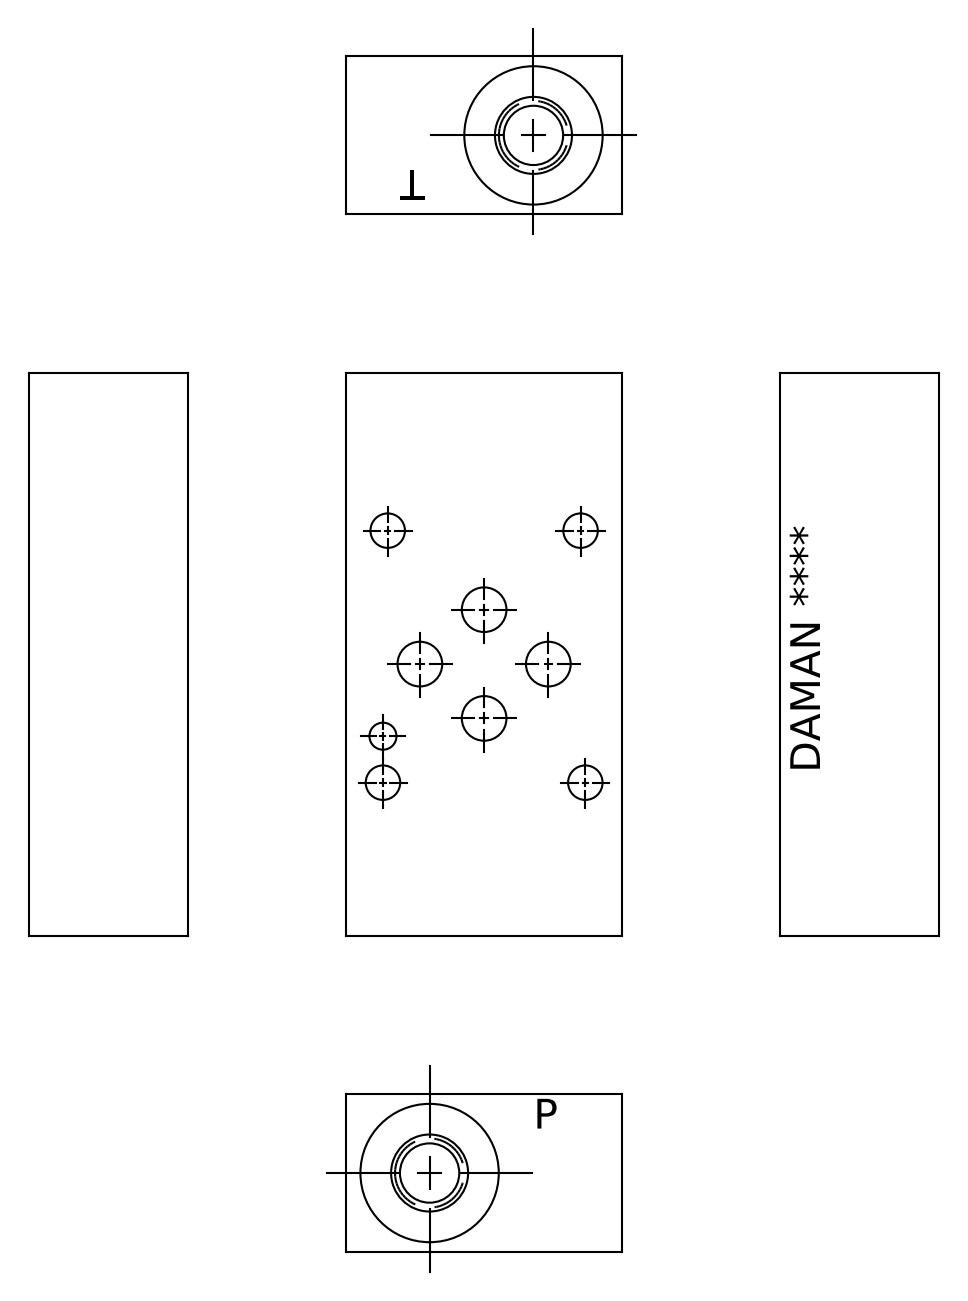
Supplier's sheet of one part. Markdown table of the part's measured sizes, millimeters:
| quantity | value |
| --- | --- |
| part name | Part_AD03TPPT4S.B00376R5_3D |
| STEP written by | Autodesk Inventor 2022 (AUTOMOTIVE_DESIGN) |
| units | millimeters |
| bodies | 1 solid, 400 faces (267 planar, 30 cylindrical, 103 other) |
| overall size | 90.5 × 44.45 × 25.4 |
| volume | 93 865 mm³ |
| surface area | 18 678 mm² |
| round holes (diameter × count) | 5.54 × 4, 7.14 × 4, 12.7 × 4, 4.78 × 2, 9.53 × 2, 9.88 × 2, 11.13 × 2, 12.4 × 2, 21.29 × 2, 3.17 × 1, 3.96 × 1 |
| main face-to-face distances | 25.4, 44.45, 90.5, 0.79, 89.71, 24.08, 1.32, 88.92, 44.41, 3.17 |
| hole center spacings | 13.52, 13.53, 22.05, 33.55, 40.5, 51.45, 7.5, 12.99 |
